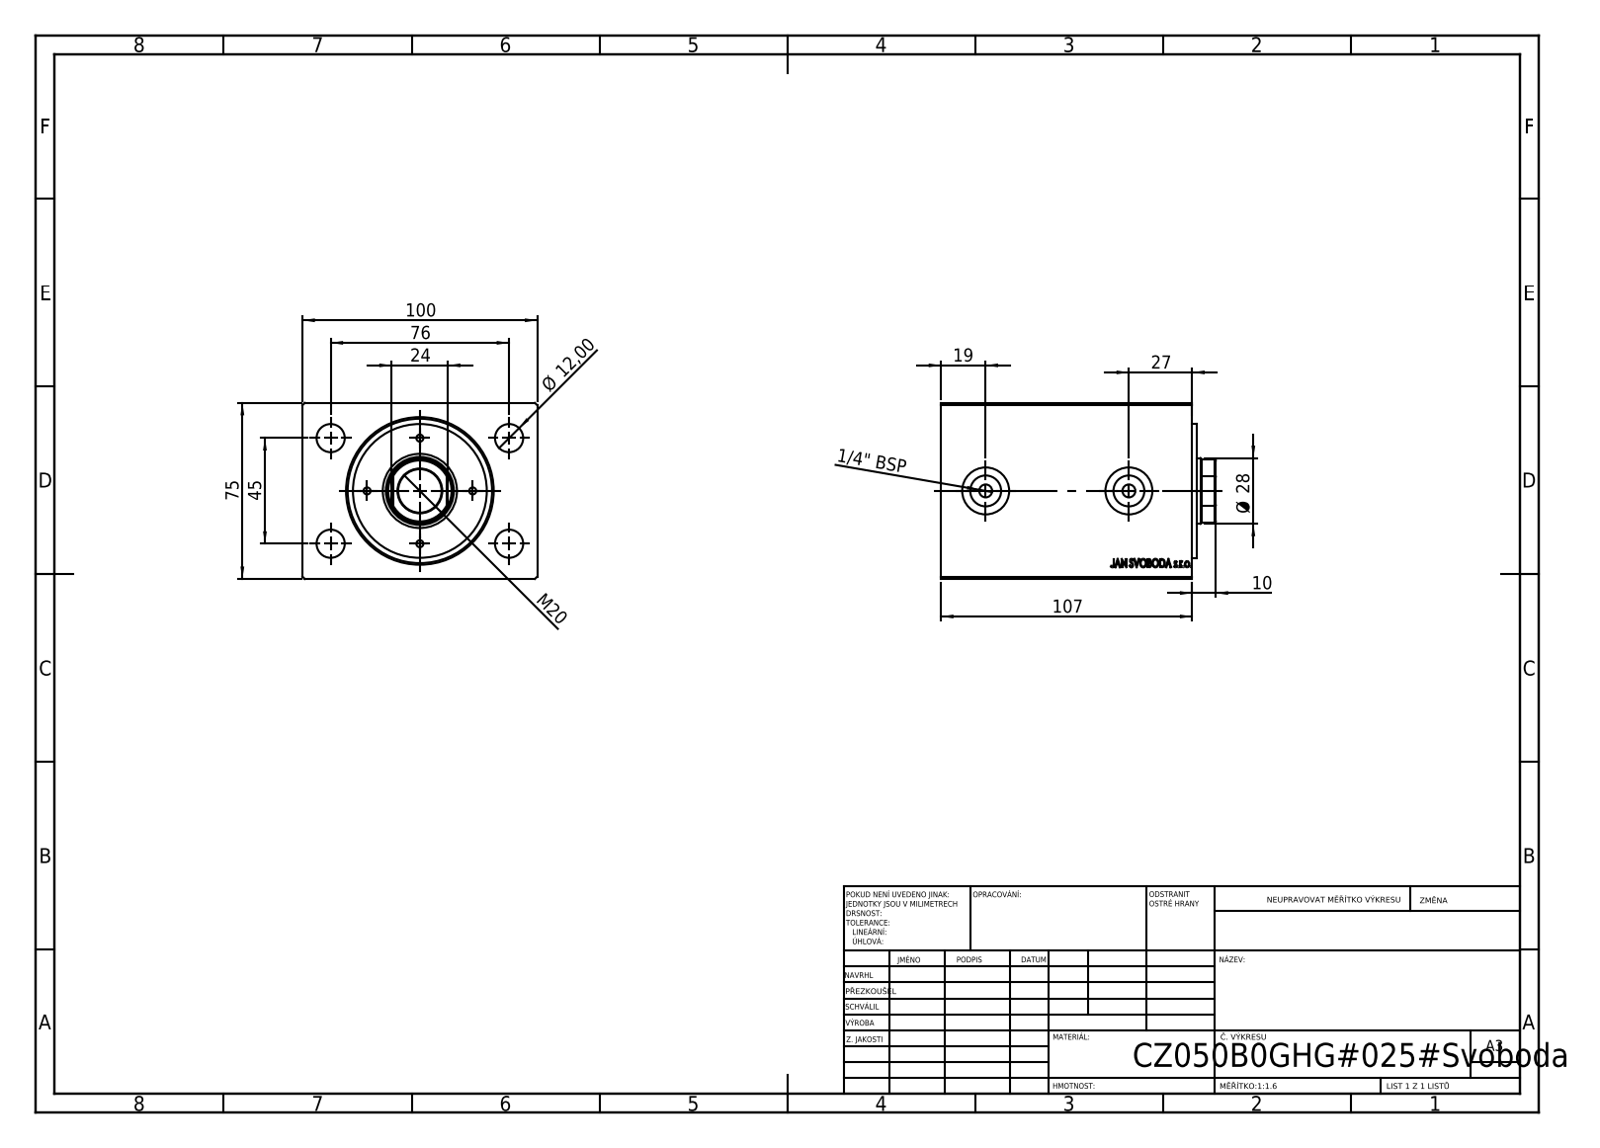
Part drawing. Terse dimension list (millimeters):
name: V500CZ_B_VC; V500CZ
written by: SolidWorks 2019 (CONFIG_CONTROL_DESIGN)
unit: mm
bodies: 3 solids, 874 faces (400 planar, 58 cylindrical, 416 other)
size: 117 × 100 × 75
volume: 737 322 mm³; area: 101 017 mm²
holes: 4× ⌀3, 4× ⌀12, 2× ⌀5.5, 2× ⌀13.16, 2× ⌀20, 1× ⌀18.5, 1× ⌀28, 1× ⌀29, 1× ⌀36, 1× ⌀50, 1× ⌀61.5
bosses: 1× ⌀57
rounds: 1× R13.5
face distances: 75, 100, 107, 89.2, 17.8, 10, 1.8, 8.2, 81, 98.8
hole spacings: 22.5, 27.32, 31.82, 38, 44.16, 45, 58.9, 64.55
